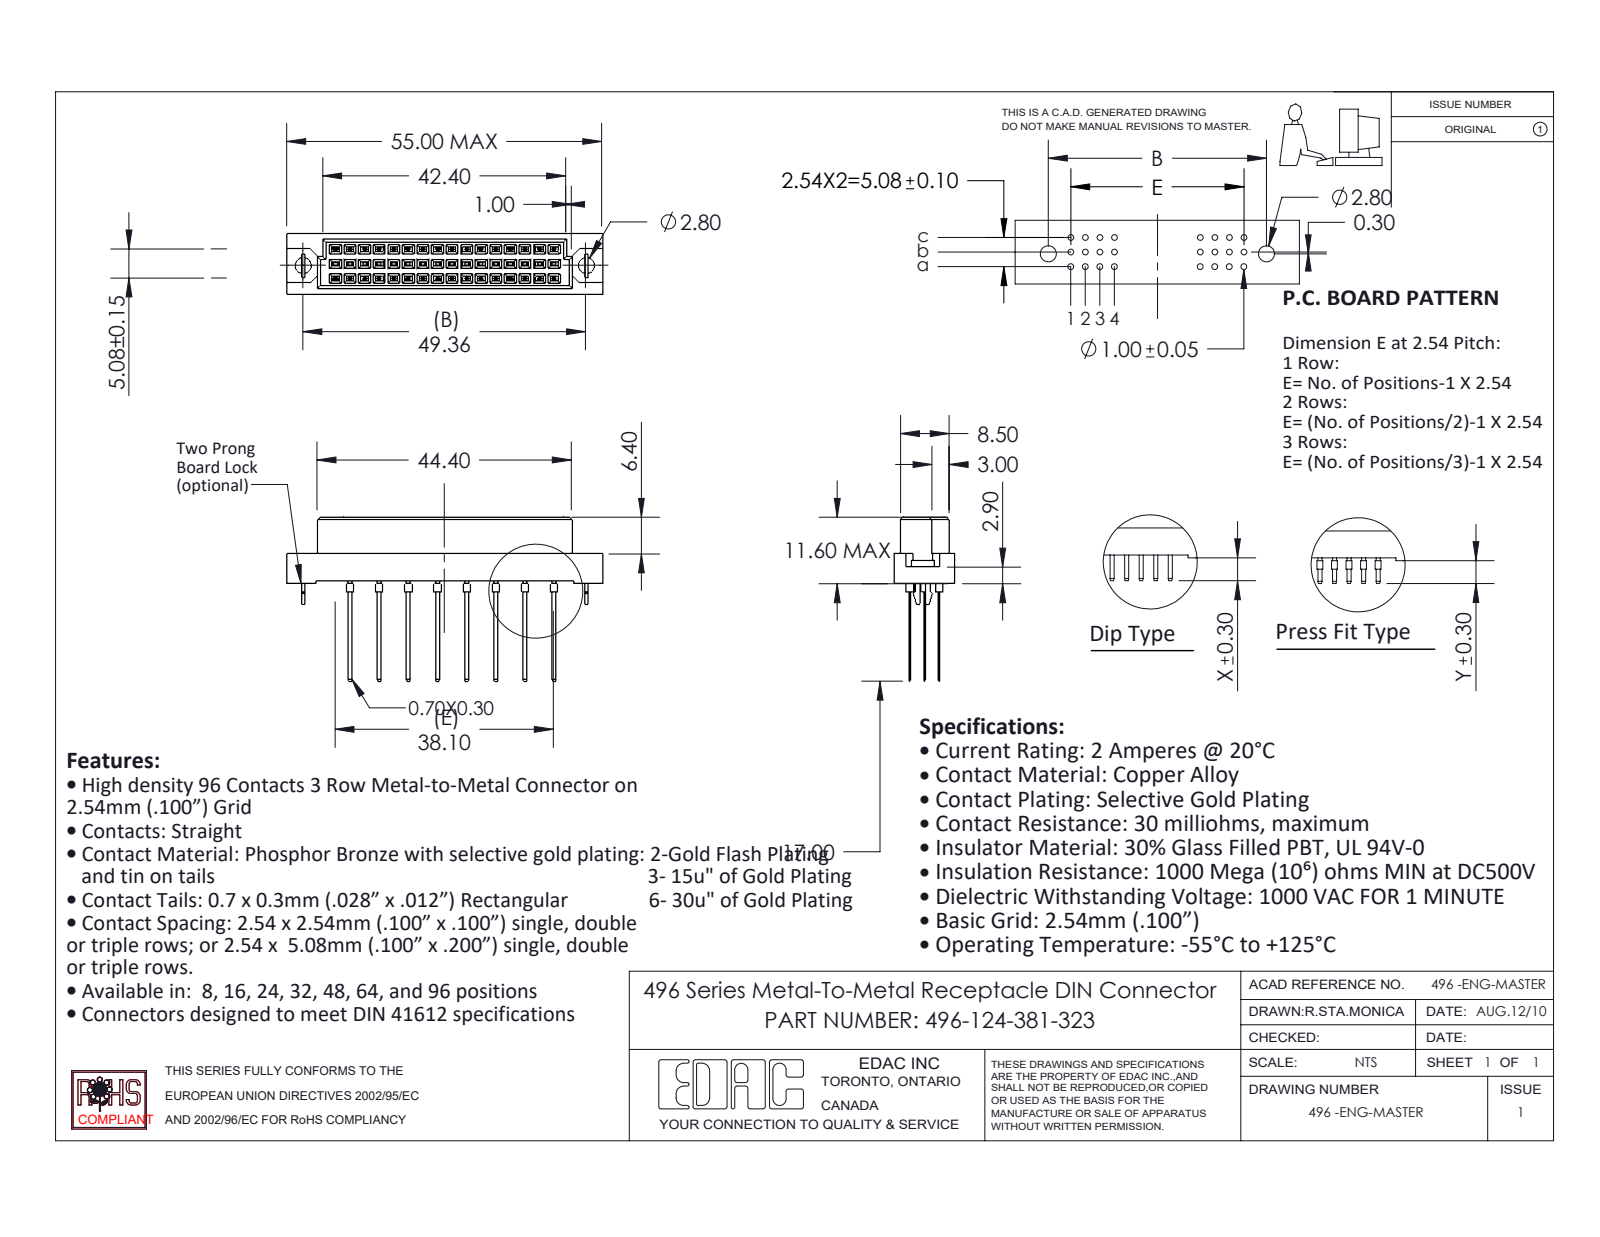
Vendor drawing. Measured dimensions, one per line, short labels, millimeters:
name: 496-124-381-323; 496 Bore-lock; 496 Part_48; 496-290_81
written by: SolidWorks 2020 (CONFIG_CONTROL_DESIGN)
unit: mm
bodies: 27 solids, 1134 faces (1080 planar, 54 cylindrical, 0 other)
size: 55 × 28.6 × 10.6
volume: 4 740 mm³; area: 5 424 mm²
holes: 2× ⌀2.8
bosses: 24× ⌀1
rounds: 1× R0.53
face distances: 2.54, 5.08, 1.05, 9.55, 0.56, 0.55, 0.81, 2.84, 4.4, 1.56
hole spacings: 49.36
